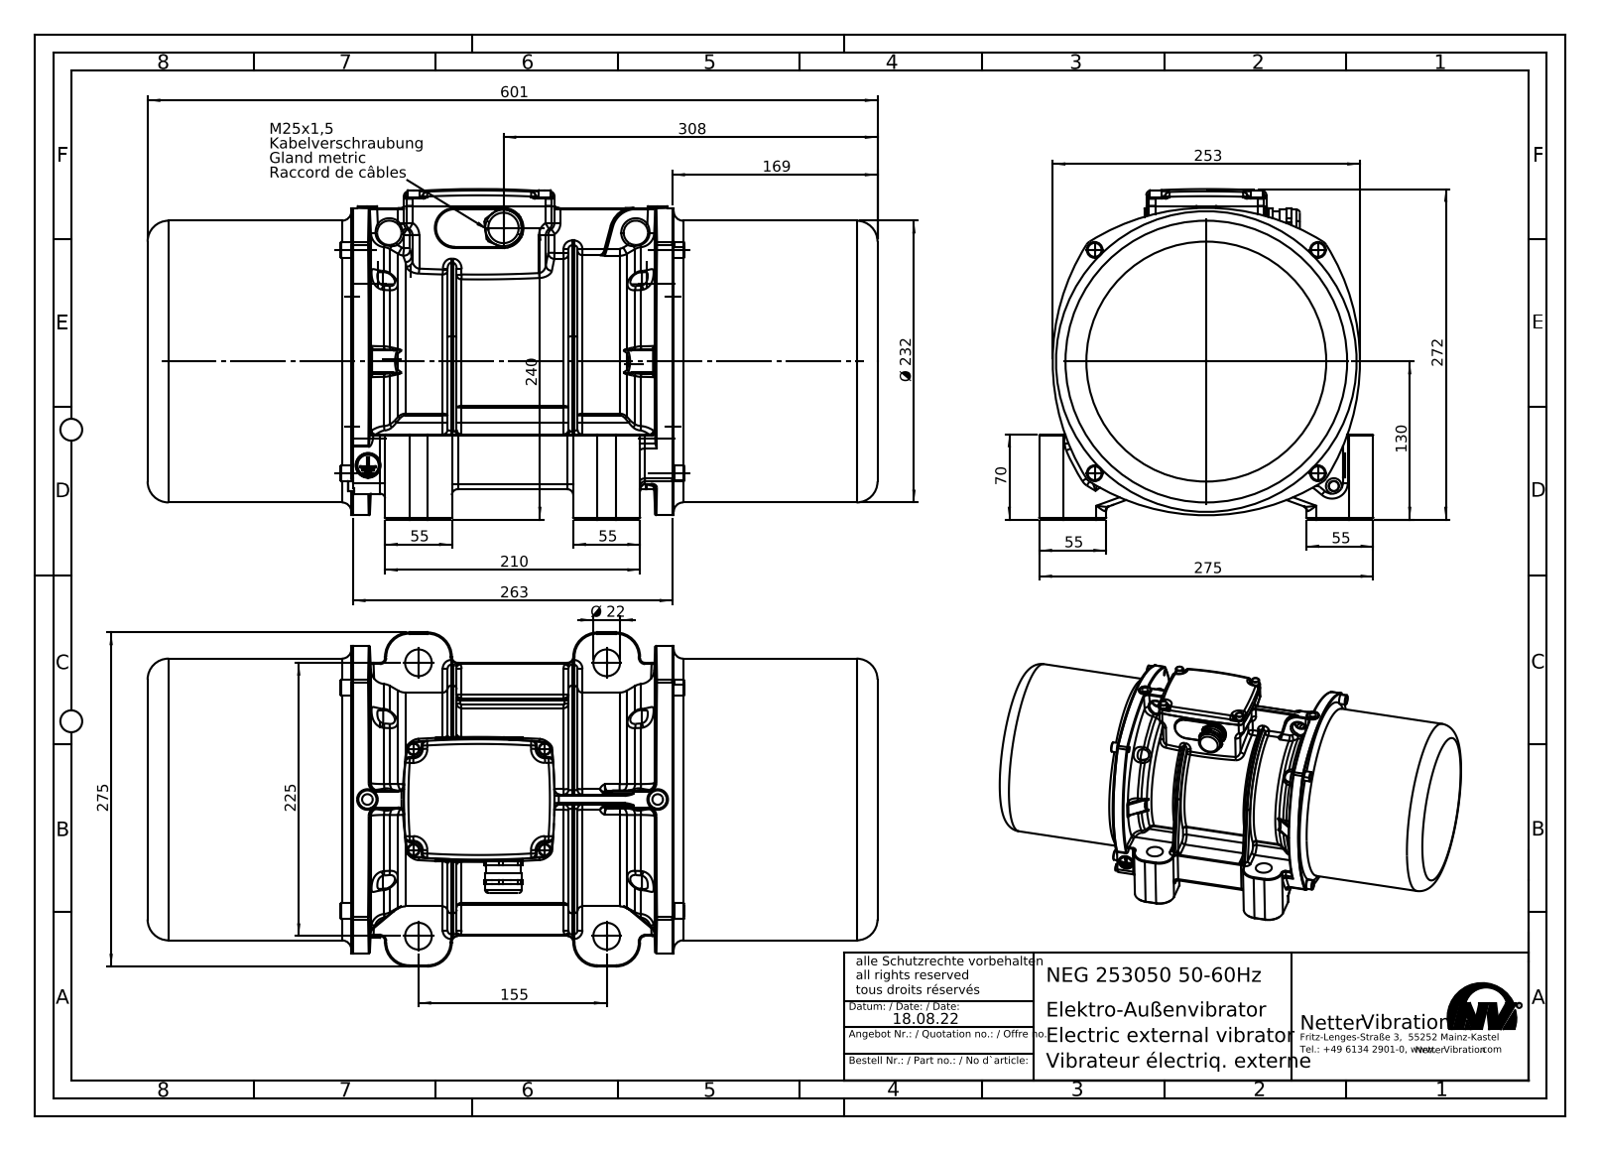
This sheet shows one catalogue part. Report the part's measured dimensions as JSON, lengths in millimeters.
{"part_name": "NEG 253050-50-60Hz", "step_written_by": "SolidWorks 2015 (AUTOMOTIVE_DESIGN)", "units": "millimeters", "bodies": {"solids": 8, "faces": 2696, "planar": 453, "cylindrical": 666, "other": 1577}, "overall_size": [601, 275, 272], "volume_mm3": 22990000, "surface_area_mm2": 1332000, "round_holes": [[22, 4], [20, 2], [100.5, 2], [13, 1], [18, 1], [25, 1], [110, 1], [114, 1], [152, 1], [210, 1], [243, 1]], "round_bosses_or_shafts": [[10, 8], [16, 4], [13, 4], [8, 4], [6, 4], [5, 2], [231.9, 1], [165, 1]], "partial_cylinders_radius": [[0.2, 102], [5, 56], [4, 55], [1, 24], [3, 20], [2, 18], [8, 17], [10, 10]], "face_to_face_distances": [169, 432, 3.5, 172.5, 428.5, 259.5, 601, 263, 256, 55], "hole_center_spacings": [136.61, 2.25, 155, 225, 273.22, 4.5, 20.16, 116.92]}
